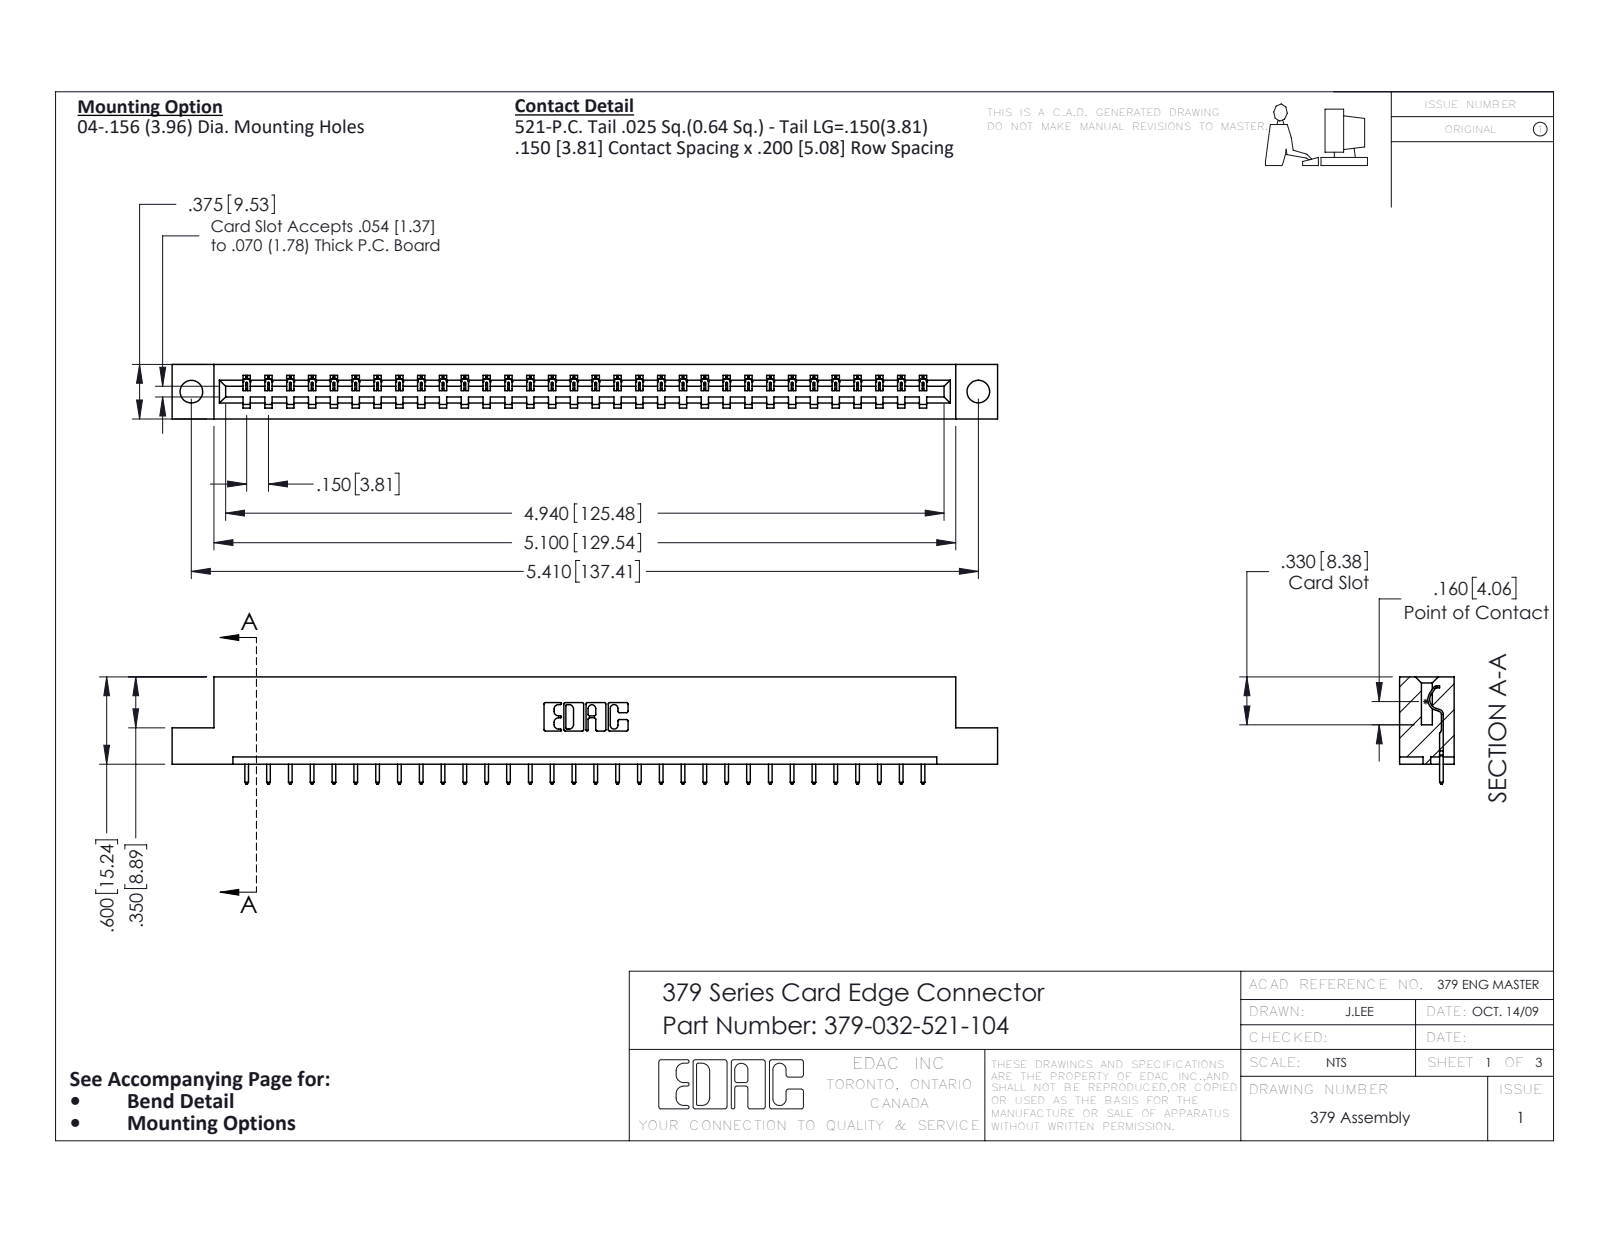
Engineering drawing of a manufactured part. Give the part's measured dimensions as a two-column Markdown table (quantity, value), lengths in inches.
| quantity | value |
| --- | --- |
| part name | 379-032-521-104; 379 Part_Flush - .156 Dia - TH; 345-292-001_345-293-121 |
| STEP written by | SolidWorks 2016 (CONFIG_CONTROL_DESIGN) |
| units | inches |
| bodies | 33 solids, 1970 faces (1414 planar, 556 cylindrical, 0 other) |
| overall size | 5.675 × 0.737 × 0.375 |
| volume | 0.906 in³ |
| surface area | 22.55 in² |
| round holes (diameter × count) | 0.156 × 2 |
| partial cylindrical surfaces (radius × count) | 0.006 × 64, 0.01 × 64, 0.01 × 22, 0.007 × 6, 0.031 × 6, 0.026 × 3, 0.014 × 1, 0.022 × 1 |
| main face-to-face distances | 0.3, 0.075, 0.375, 0.225, 0.6, 0.2, 0.275, 0.1, 0.025, 0.55 |
| hole center spacings | 5.41 |
